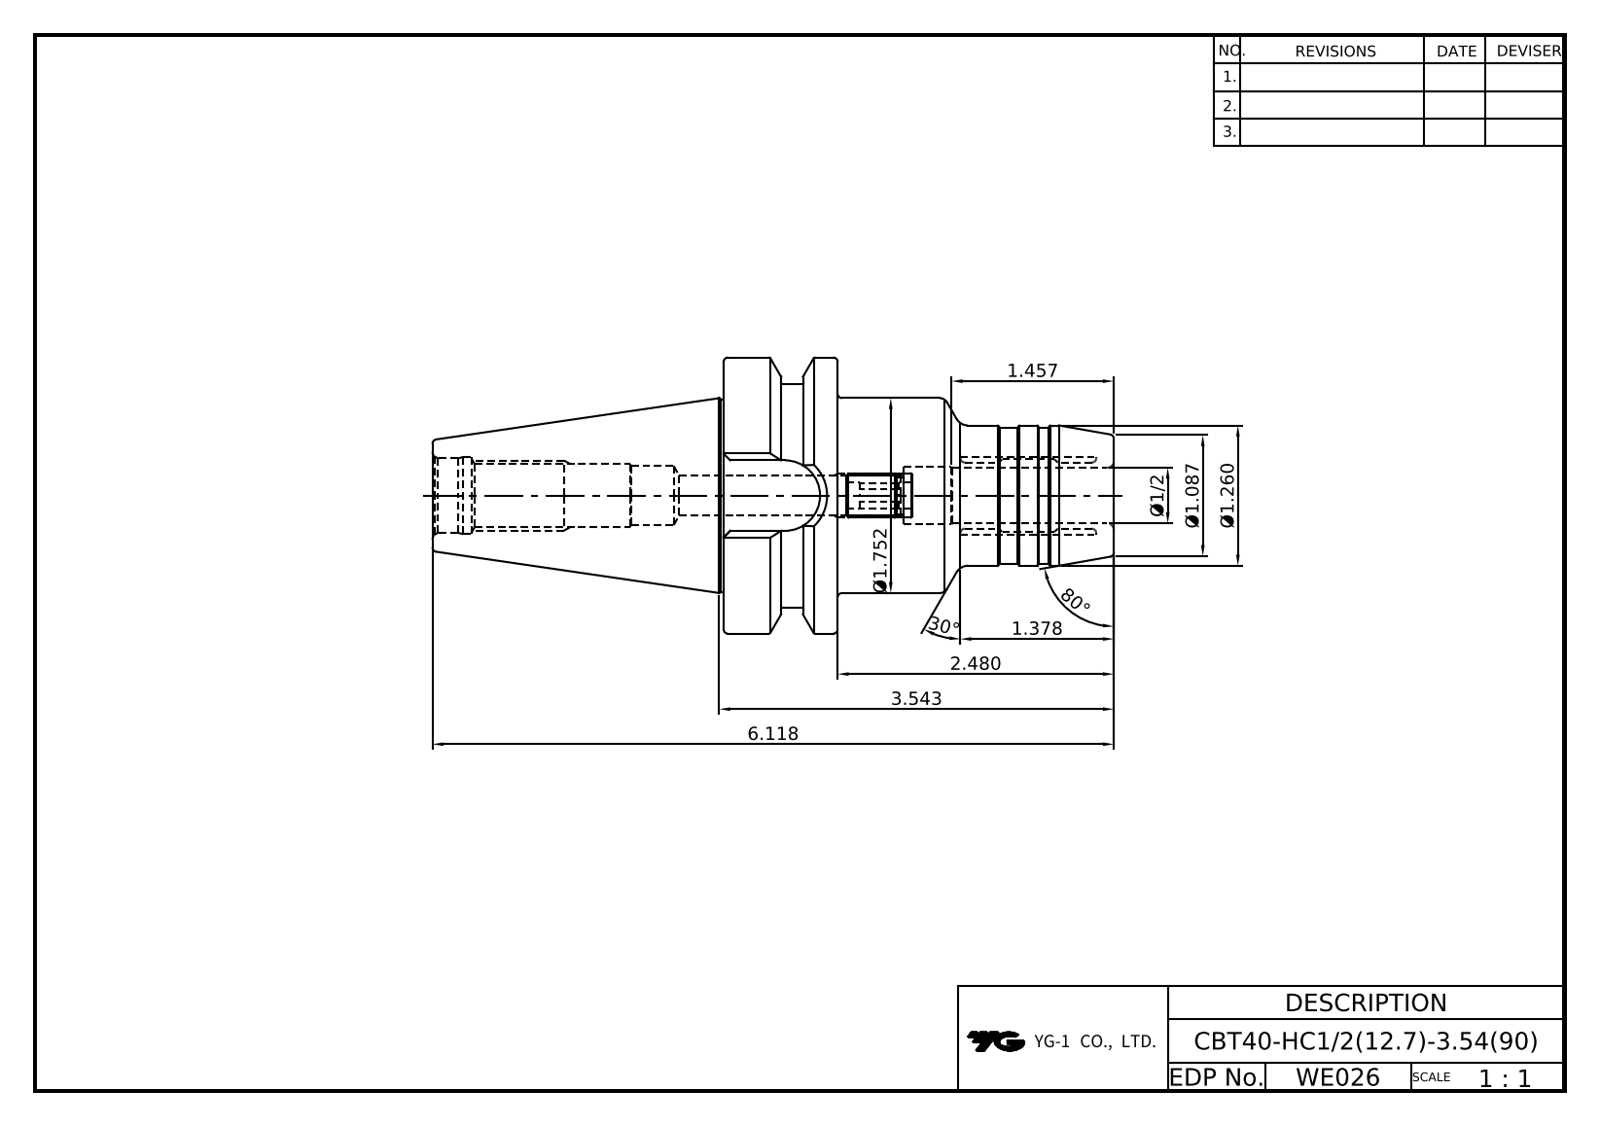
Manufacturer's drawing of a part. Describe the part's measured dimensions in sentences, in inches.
The part is named "LO-CBT40-HC12.7-3.54". Its 3-D file was written by "Autodesk Inventor 2024 (AUTOMOTIVE_DESIGN)". It is 1 solid with 83 faces: 24 planar, 21 cylindrical and 38 other. Overall it measures 6.118 by 2.48 by 2.48 inches. Its volume is 11.28 cubic inches and its surface area 48.52 square inches. Round holes: 1 of diameter 0.351, 1 of diameter 0.5, 1 of diameter 0.524, 1 of diameter 0.531, 1 of diameter 0.545, 1 of diameter 0.669, 1 of diameter 0.693. Round bosses or shafts: 1 of diameter 2.48, 1 of diameter 2.008, 1 of diameter 1.752, 1 of diameter 1.732, 1 of diameter 1.26, 1 of diameter 1.22. Partial cylindrical surfaces (rounded edges, fillets, slot ends): 1 of radius 0.317. The main face-to-face distances are 1.024, 3.504, 2.48, 1.78, 0.197, 0.713, 0.311, 2.791, 0.516, 0.508.
